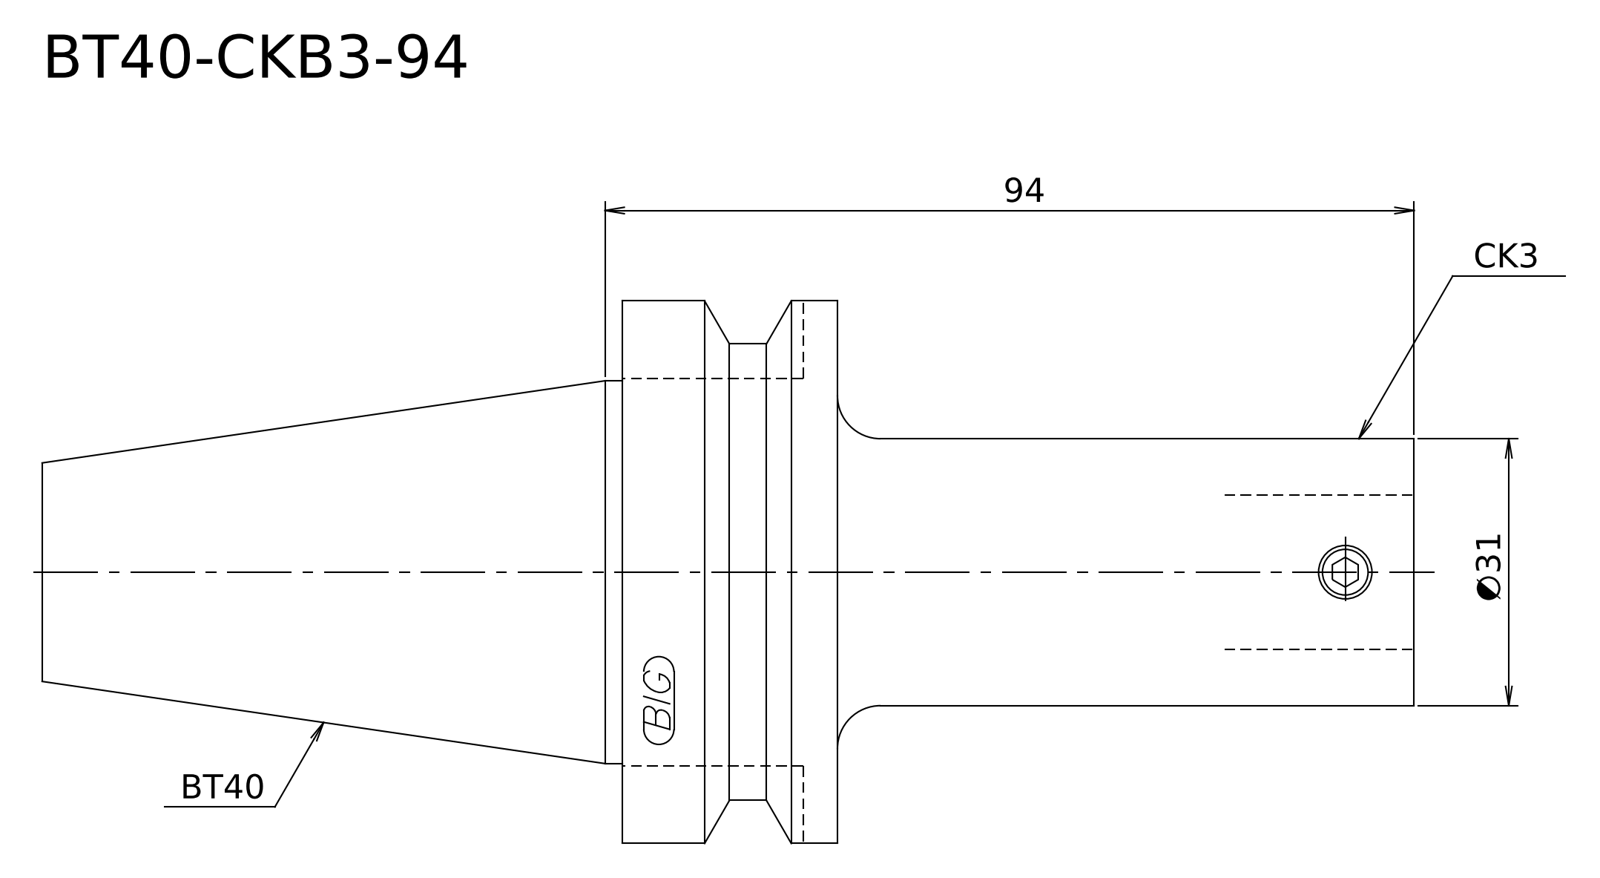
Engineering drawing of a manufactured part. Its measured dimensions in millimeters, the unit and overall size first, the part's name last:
Units: millimetres
Overall size (bounding box): 159.4 × 63 × 63
Round bosses / shafts (diameter × count): ⌀63 ×1, ⌀53 ×1, ⌀44.45 ×1, ⌀31 ×1
Main face-to-face distances: 25, 67, 92, 159.4, 92.4, 67.4
Volume: 190 535 mm³ · Surface area: 24 722 mm²
Bodies: 1 solid, 14 faces (4 planar, 5 cylindrical, 5 other)
STEP written by: Kubotek KeyCreator V8.5.1 (14335) (CONFIG_CONTROL_DESIGN)
